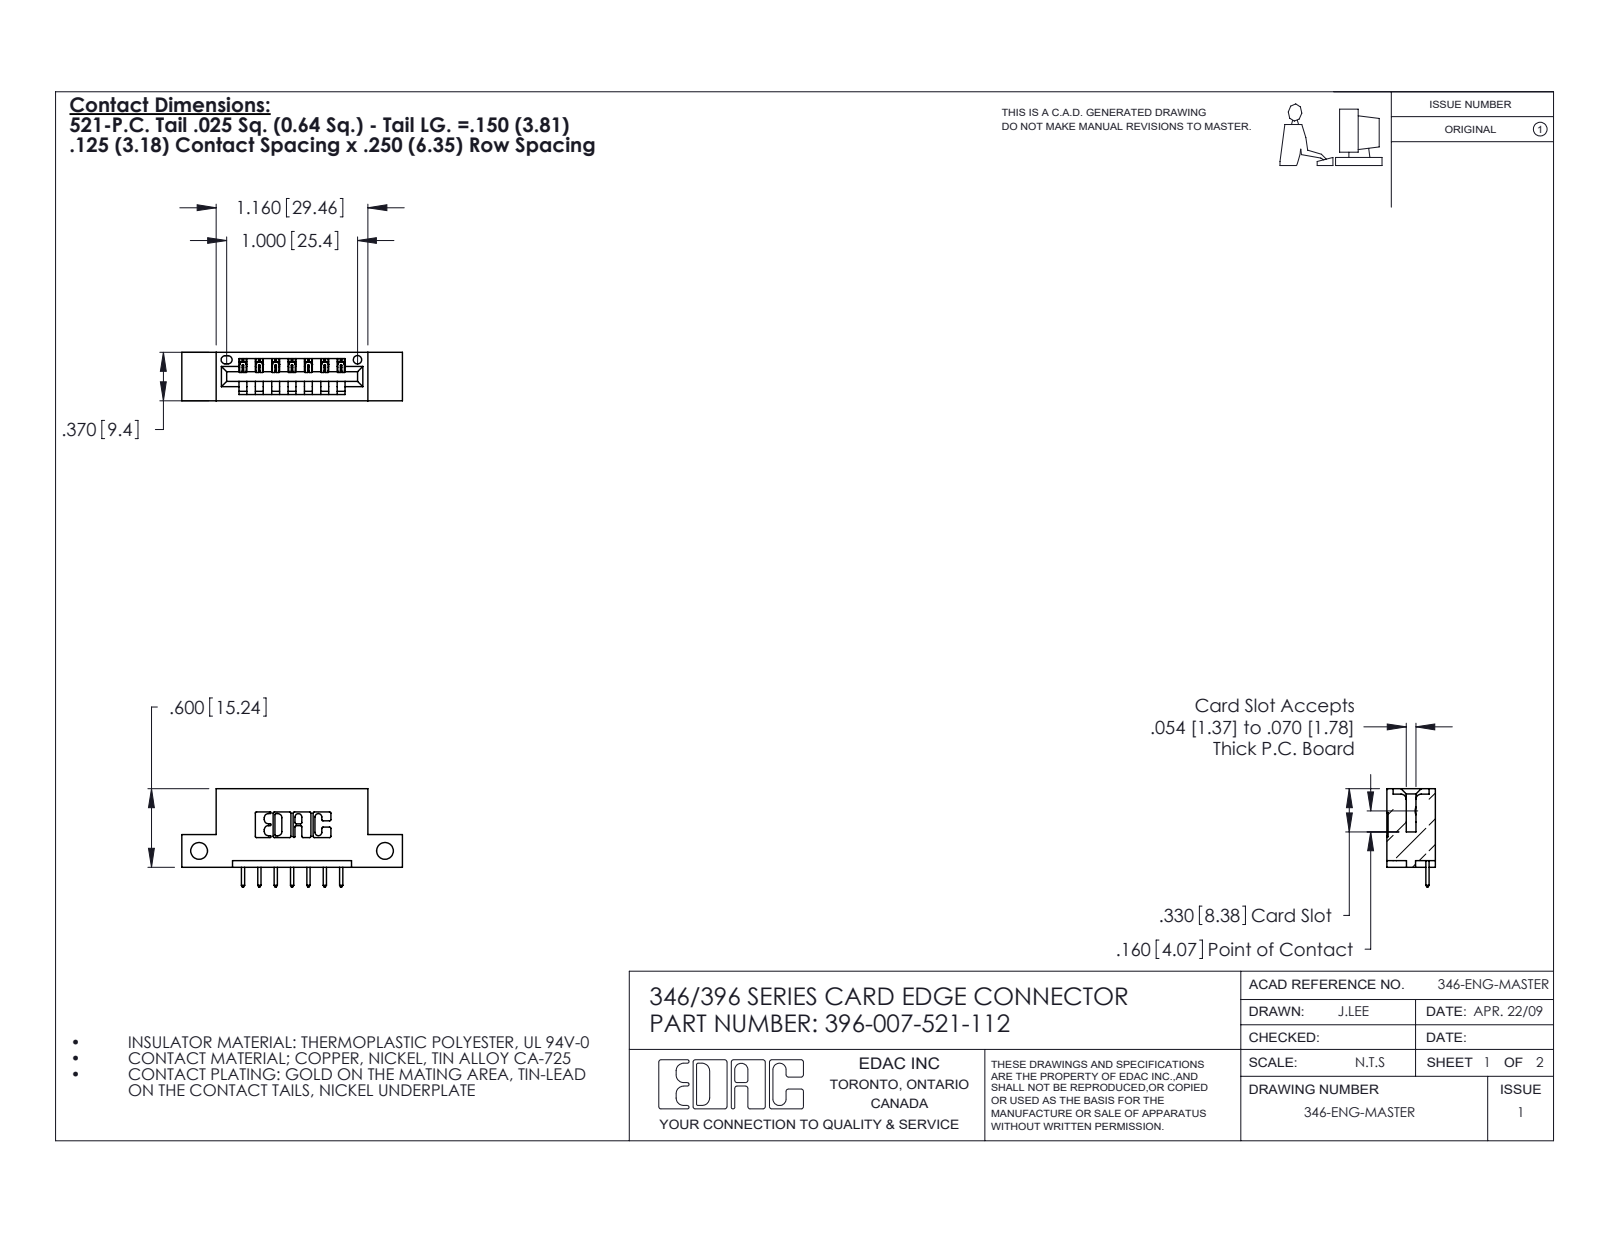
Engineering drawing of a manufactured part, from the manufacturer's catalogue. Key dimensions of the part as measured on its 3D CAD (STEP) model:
Part name (STEP PRODUCT): 346 Part_Flush Mounting Lugs - Side Mount; 345-292-001_345-293-121; 396-007-521-112
STEP written by: SolidWorks 2020 (CONFIG_CONTROL_DESIGN)
Units: inches
Bodies: 8 solids, 528 faces (356 planar, 172 cylindrical, 0 other)
Overall size (bounding box): 1.685 × 0.75 × 0.37
Volume: 0.229 in³ · Surface area: 6.328 in²
Round holes (diameter × count): ⌀0.128 ×2, ⌀0.064 ×1
Partial cylindrical surfaces — rounded edges, fillets, slot ends (radius × count): R0.01 ×22, R0.006 ×14, R0.01 ×14, R0.007 ×6, R0.031 ×6, R0.026 ×3, R0.031 ×2, R0.04 ×2
Main face-to-face distances: 0.25, 0.37, 0.048, 0.322, 0.148, 0.222, 0.1, 0.174, 0.125, 0.185
Hole centre spacings: 1.42
